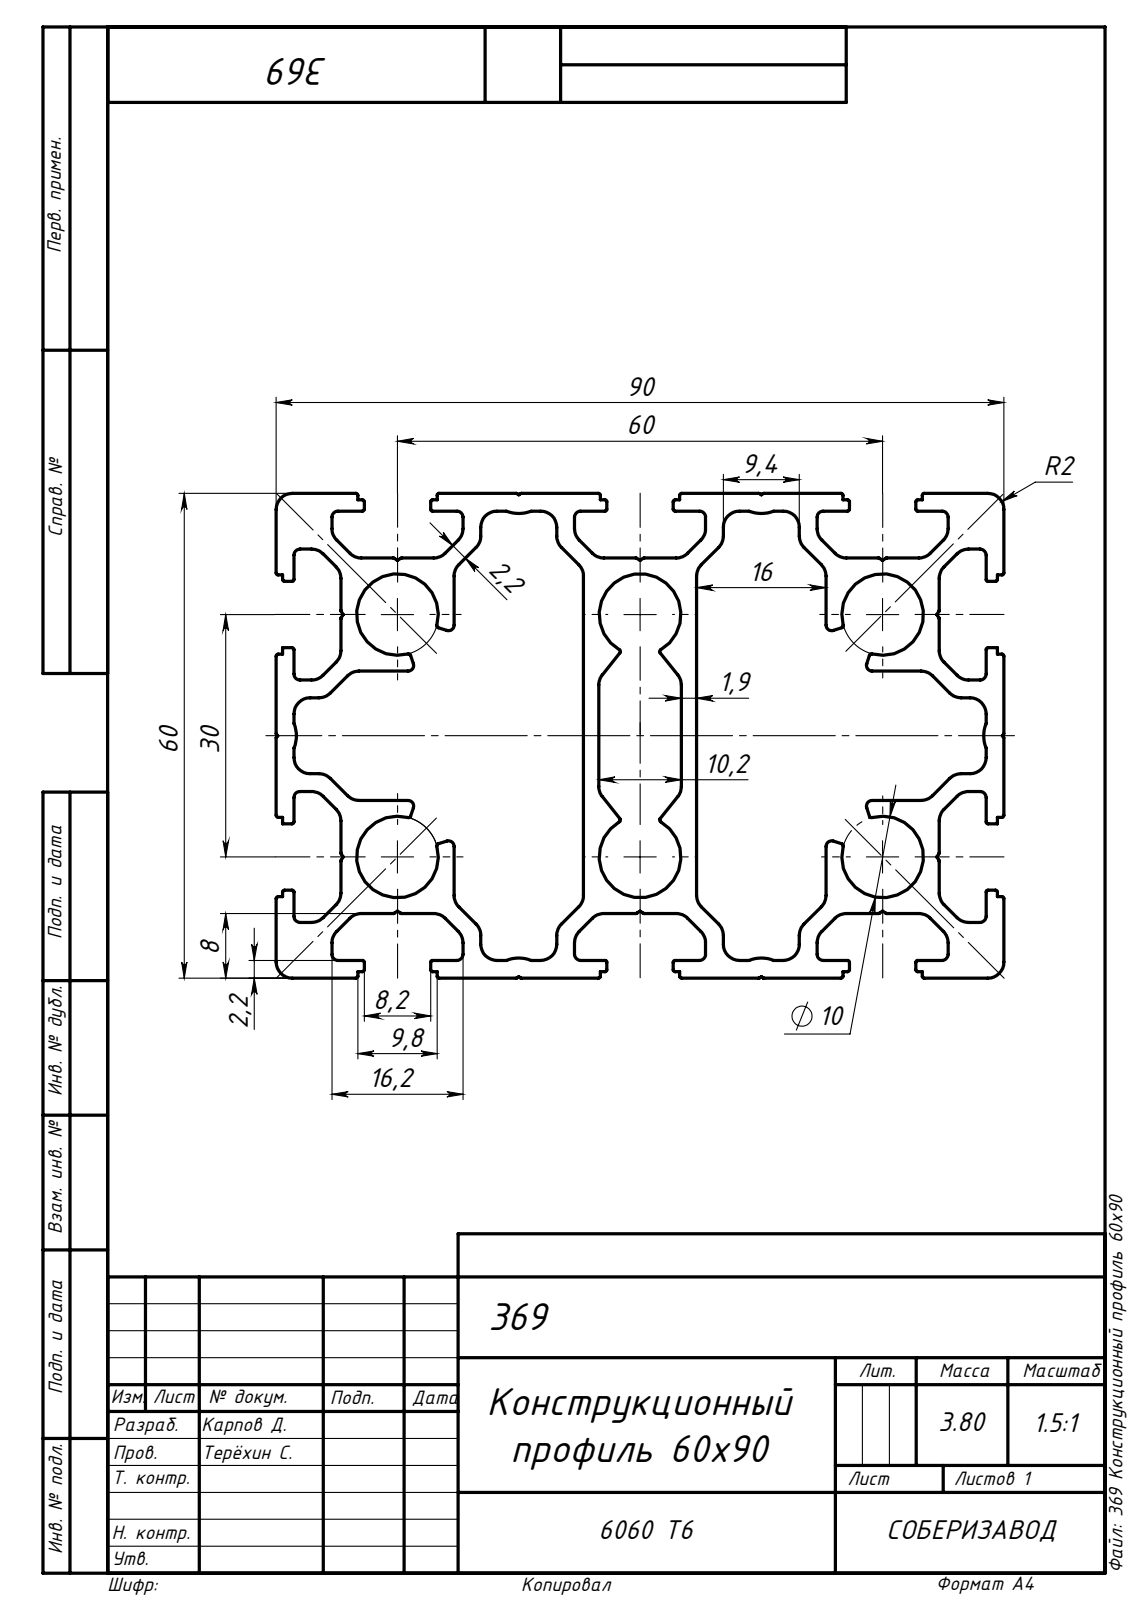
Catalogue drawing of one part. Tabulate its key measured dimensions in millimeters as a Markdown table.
| quantity | value |
| --- | --- |
| part name | 369 Конструкционный профиль 60х90 |
| STEP written by | SolidWorks 2014 (AUTOMOTIVE_DESIGN) |
| units | millimeters |
| bodies | 1 solid, 494 faces (254 planar, 240 cylindrical, 0 other) |
| overall size | 1000 × 90 × 60 |
| volume | 1 409 000 mm³ |
| surface area | 1 085 000 mm² |
| round holes (diameter × count) | 10.1 × 6 |
| partial cylindrical surfaces (radius × count) | 0.25 × 96, 2 × 84, 0.75 × 20, 0.7 × 8, 4 × 6 |
| main face-to-face distances | 52, 2.2, 30, 38, 14, 60, 8, 5.8, 49.8, 44 |
| hole center spacings | 30, 42.43, 60, 67.08 |
